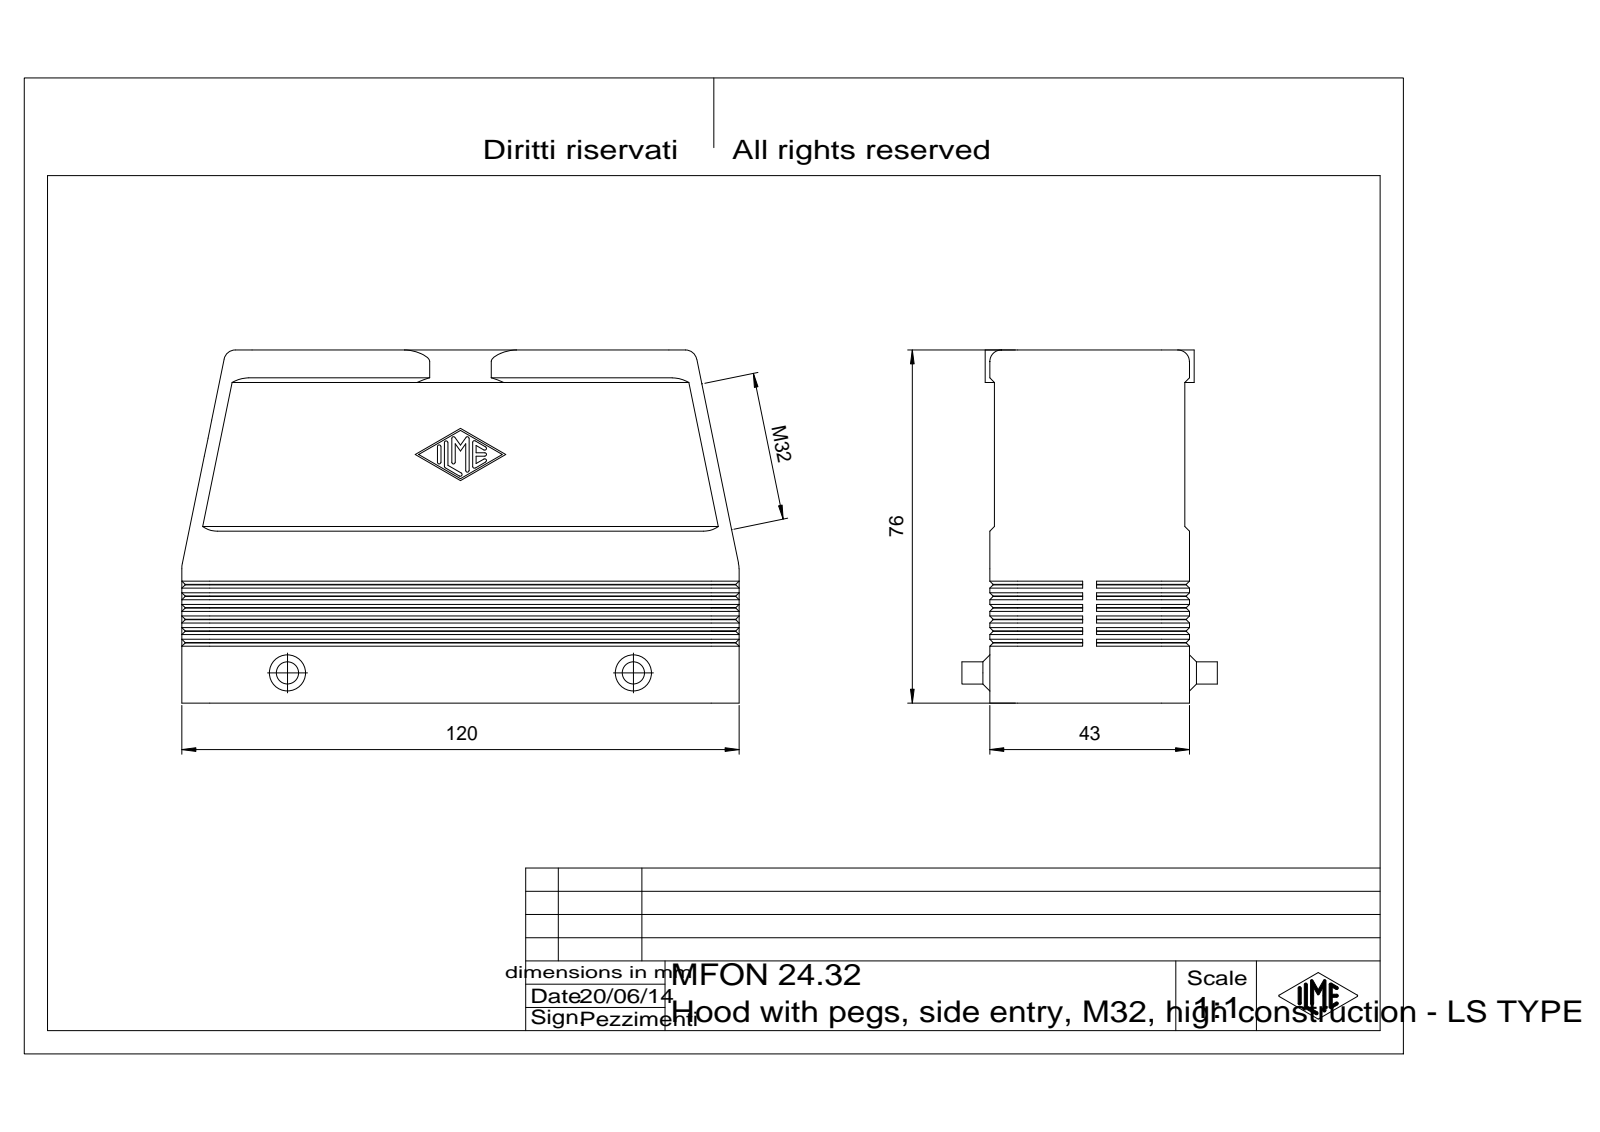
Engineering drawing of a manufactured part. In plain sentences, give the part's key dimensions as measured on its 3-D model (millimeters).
The part is named "MFON_24.32". Its 3-D file was written by "CoCreate Modeling 16.00A 16-Aug-2008 (C) Parametric Technology GmbH (AUTOMOTIVE_DESIGN)". It is 1 solid with 415 faces: 197 planar, 146 cylindrical and 72 other. Overall it measures 120 by 76 by 55 millimeters. Its volume is 98 433 cubic millimeters and its surface area 52 953 square millimeters. Round holes: 4 of diameter 2.46, 4 of diameter 4, 1 of diameter 32. Round bosses or shafts: 2 of diameter 4.8. Partial cylindrical surfaces (rounded edges, fillets, slot ends): 10 of radius 6, 4 of radius 2, 4 of radius 2.5, 4 of radius 3, 4 of radius 5.3, 1 of radius 22.5. The main face-to-face distances are 4, 35, 38, 3, 1, 39, 42, 41, 43, 7. The hole center spacings are 27, 104, 107.45.
